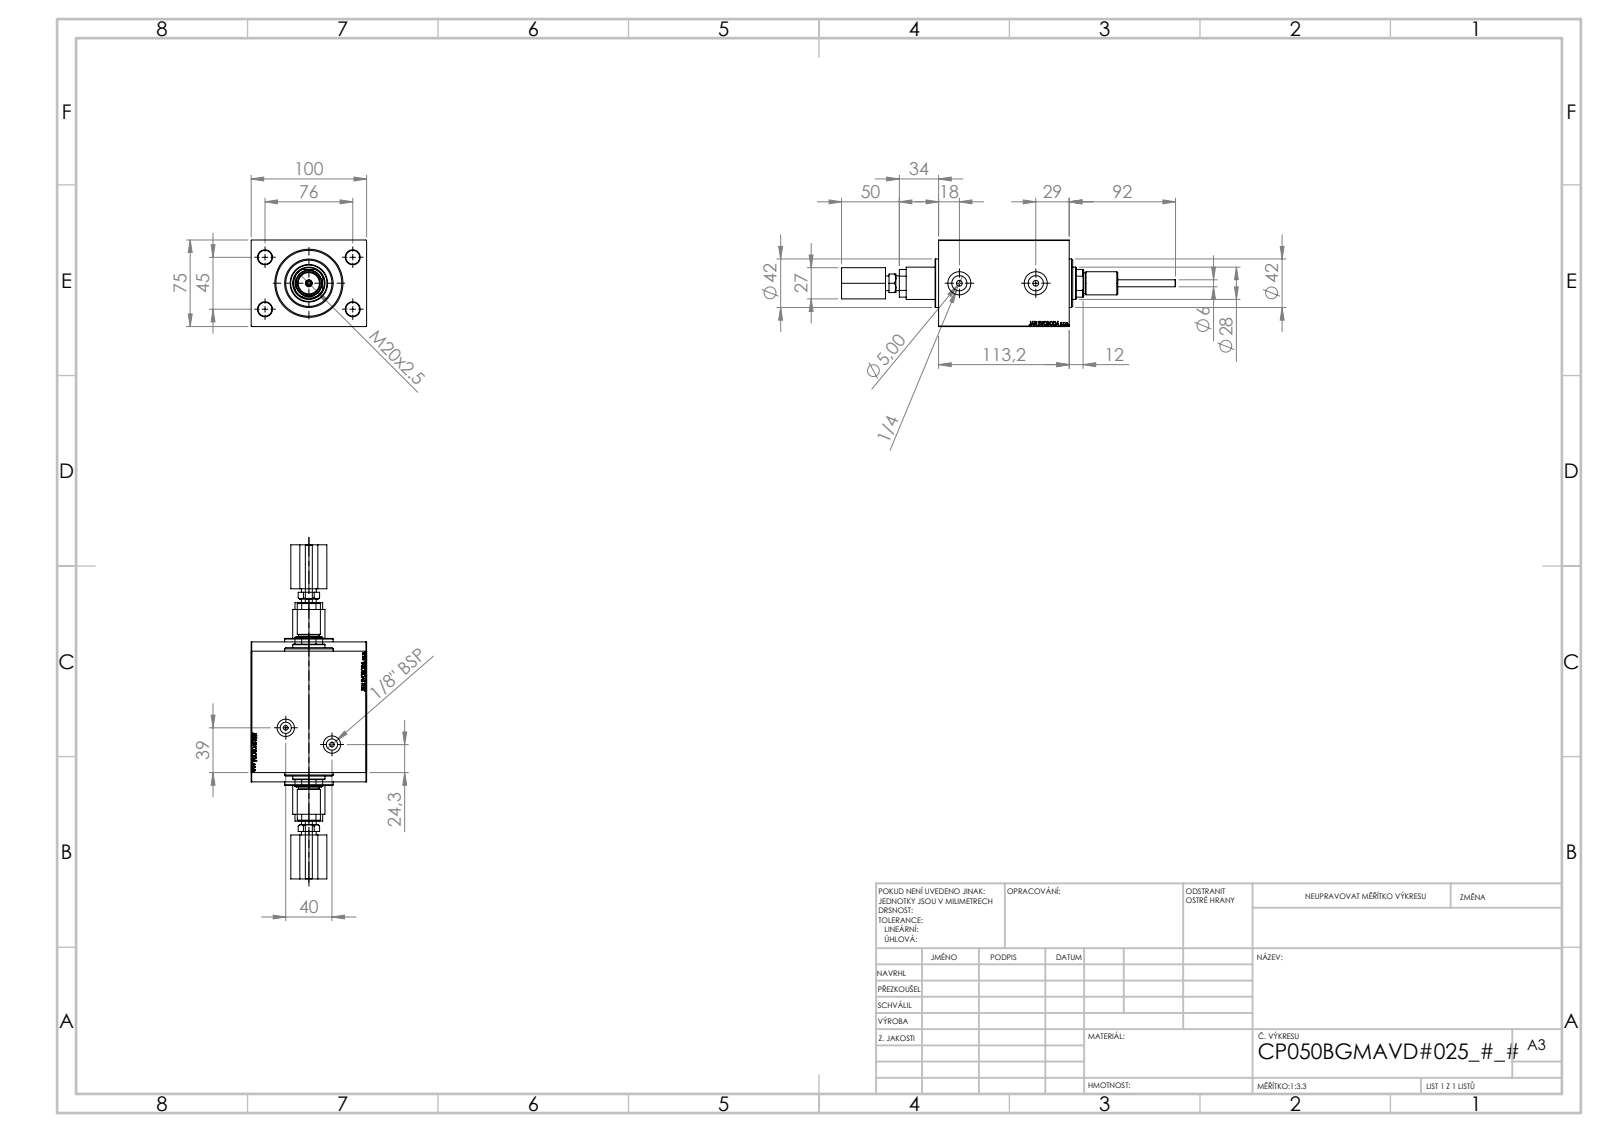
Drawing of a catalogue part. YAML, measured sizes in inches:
part_name: "V450DCP_VC_B; V450DCP_B_Body; V450DCP_B_RodCooling_ACCESSORIES; V450CP_MALE_METRIC (+1 more)"
step_written_by: "SolidWorks 2019 (CONFIG_CONTROL_DESIGN)"
units: inches
bodies: {solids: 5, faces: 986, planar: 438, cylindrical: 98, other: 450}
overall_size: [11.386, 3.937, 2.953]
volume: 51.82
surface_area: 205.6
round_holes:
  - {diameter: 0.472, count: 4}
  - {diameter: 0.157, count: 2}
  - {diameter: 0.197, count: 2}
  - {diameter: 0.383, count: 2}
  - {diameter: 0.518, count: 2}
  - {diameter: 0.591, count: 2}
  - {diameter: 0.787, count: 2}
  - {diameter: 0.118, count: 1}
  - {diameter: 0.236, count: 1}
  - {diameter: 0.728, count: 1}
  - {diameter: 1.102, count: 1}
  - {diameter: 1.24, count: 1}
round_bosses_or_shafts:
  - {diameter: 1.654, count: 1}
  - {diameter: 0.787, count: 1}
  - {diameter: 0.709, count: 1}
  - {diameter: 0.503, count: 1}
partial_cylinders:
  - {radius: 0.531, count: 1}
face_to_face_distances: [2.953, 3.937, 4.457, 0.551, 3.906, 1.693, 0.039, 1.063, 0.512, 4.417]
hole_center_spacings: [1.739, 1.772, 2.992, 3.477, 1.675, 2.606]
